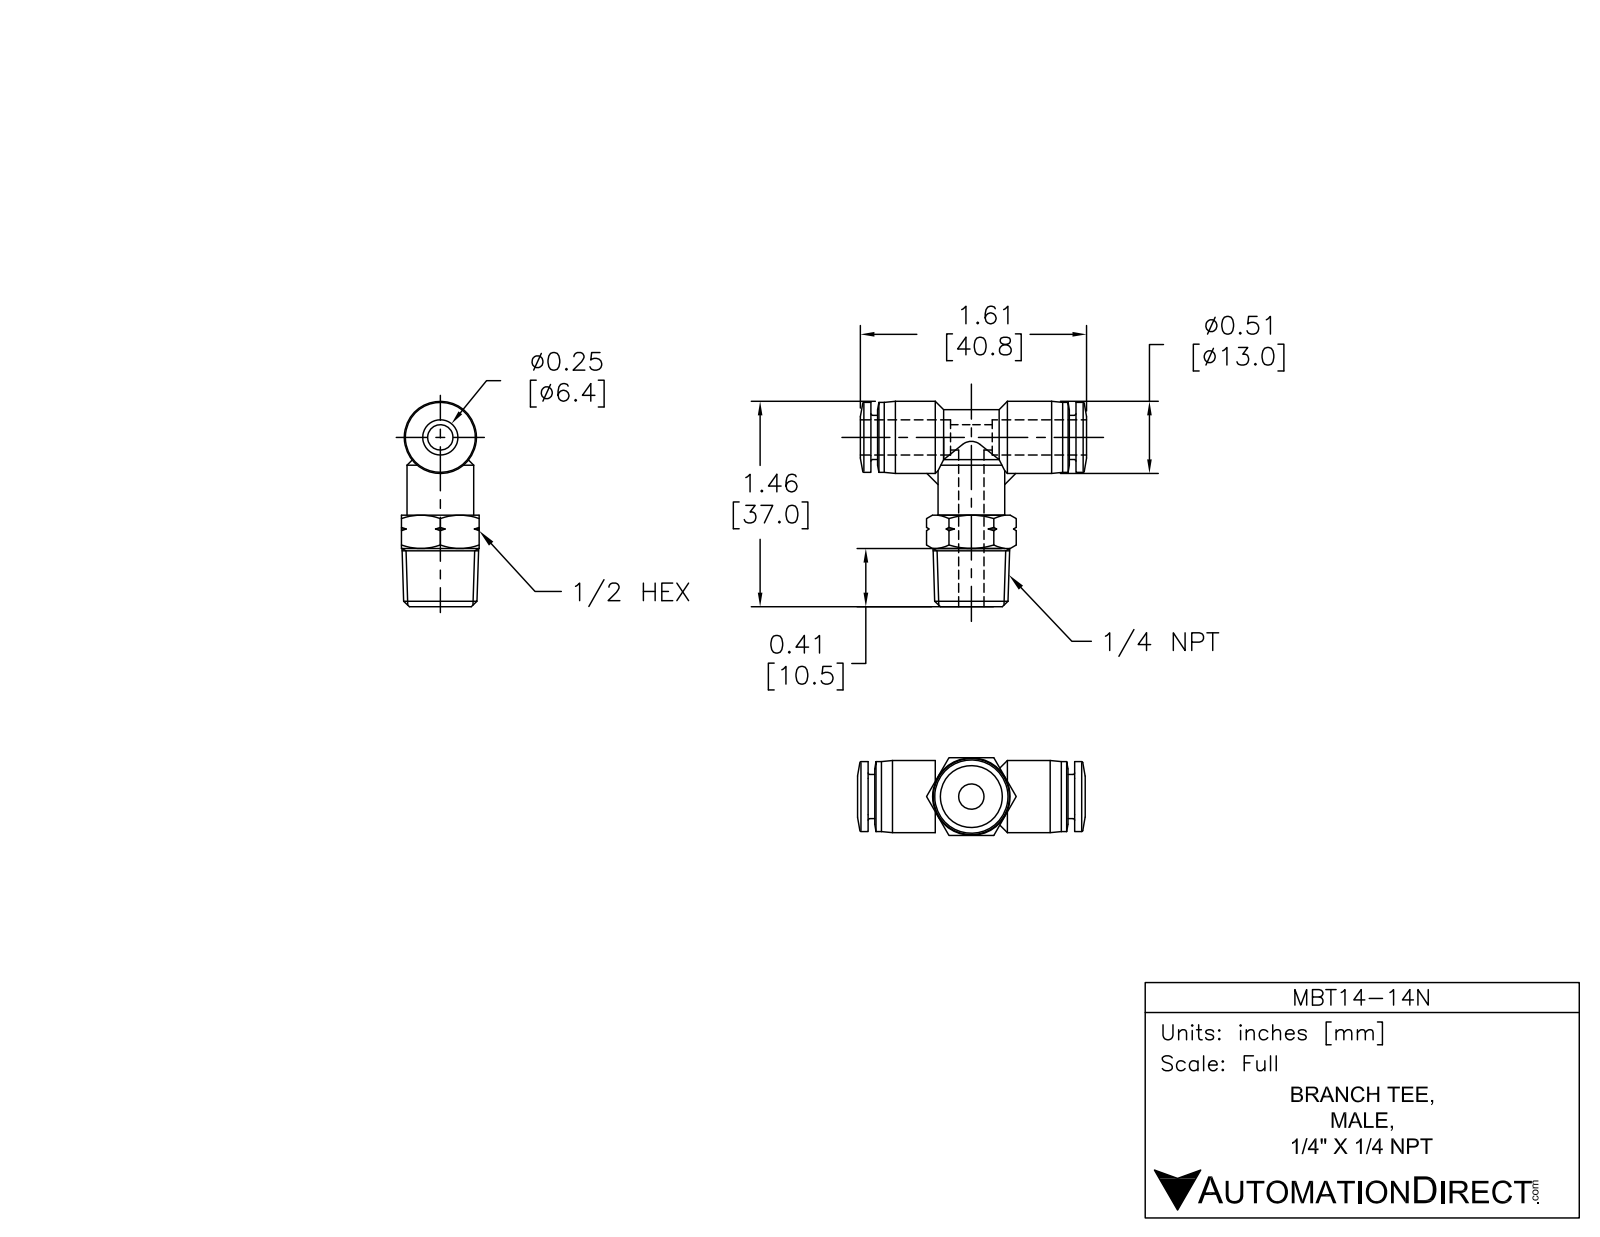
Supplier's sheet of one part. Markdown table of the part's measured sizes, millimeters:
| quantity | value |
| --- | --- |
| part name | MBT14-14N |
| STEP written by | SolidWorks 2015 (AUTOMOTIVE_DESIGN) |
| units | millimeters |
| bodies | 1 solid, 118 faces (21 planar, 31 cylindrical, 66 other) |
| overall size | 41 × 37 × 14 |
| volume | 6 370 mm³ |
| surface area | 4 381 mm² |
| round holes (diameter × count) | 4.5 × 2, 6.6 × 1 |
| round bosses / shafts (diameter × count) | 13 × 1, 12.6 × 1, 12 × 1, 10 × 1, 8 × 1 |
| partial cylindrical surfaces (radius × count) | 5 × 1 |
| main face-to-face distances | 14, 37.2, 1.2, 36, 16.5, 14.9, 22.3, 13.7, 21.1, 34.8 |
